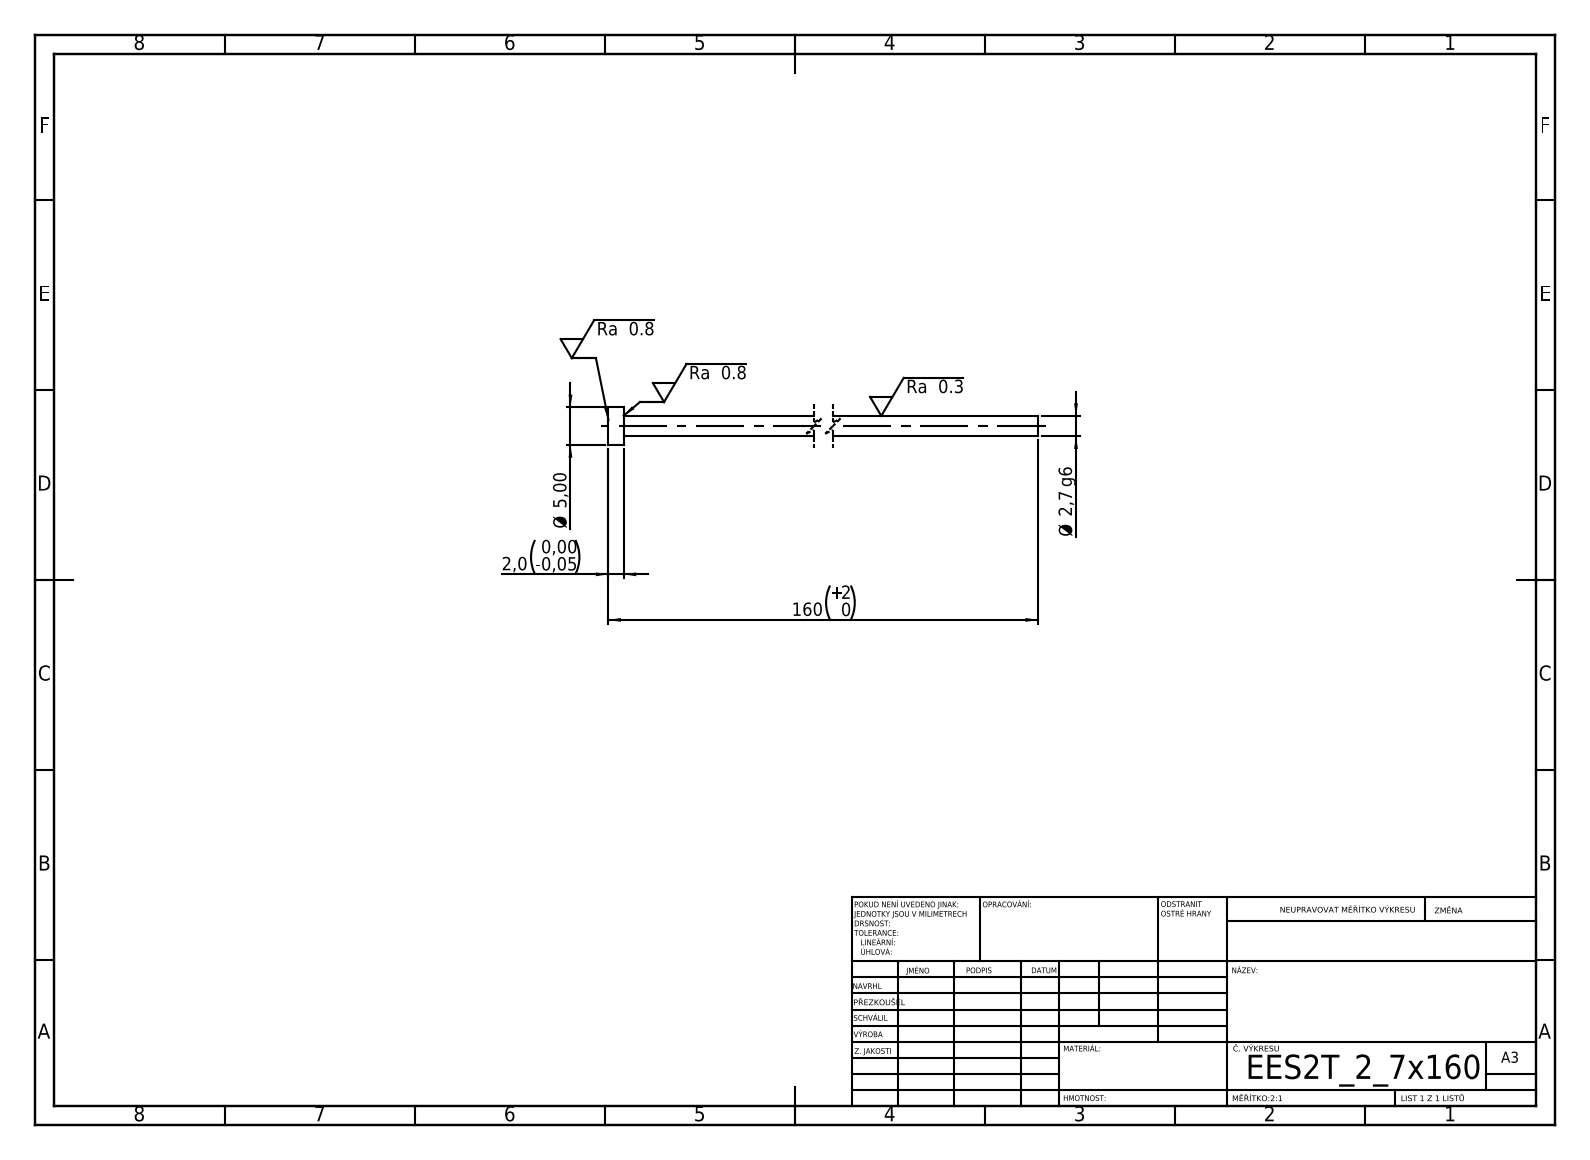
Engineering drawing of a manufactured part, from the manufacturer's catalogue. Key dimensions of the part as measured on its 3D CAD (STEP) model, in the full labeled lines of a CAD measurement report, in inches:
STEP written by: SolidWorks 2019 (CONFIG_CONTROL_DESIGN)
Units: inches
Bodies: 1 solid, 7 faces (3 planar, 4 cylindrical, 0 other)
Overall size (bounding box): 6.299 × 0.197 × 0.197
Volume: 0.058 in³ · Surface area: 2.187 in²
Round bosses / shafts (diameter × count): ⌀0.197 ×1, ⌀0.106 ×1
Main face-to-face distances: 0.079, 6.299, 6.22
